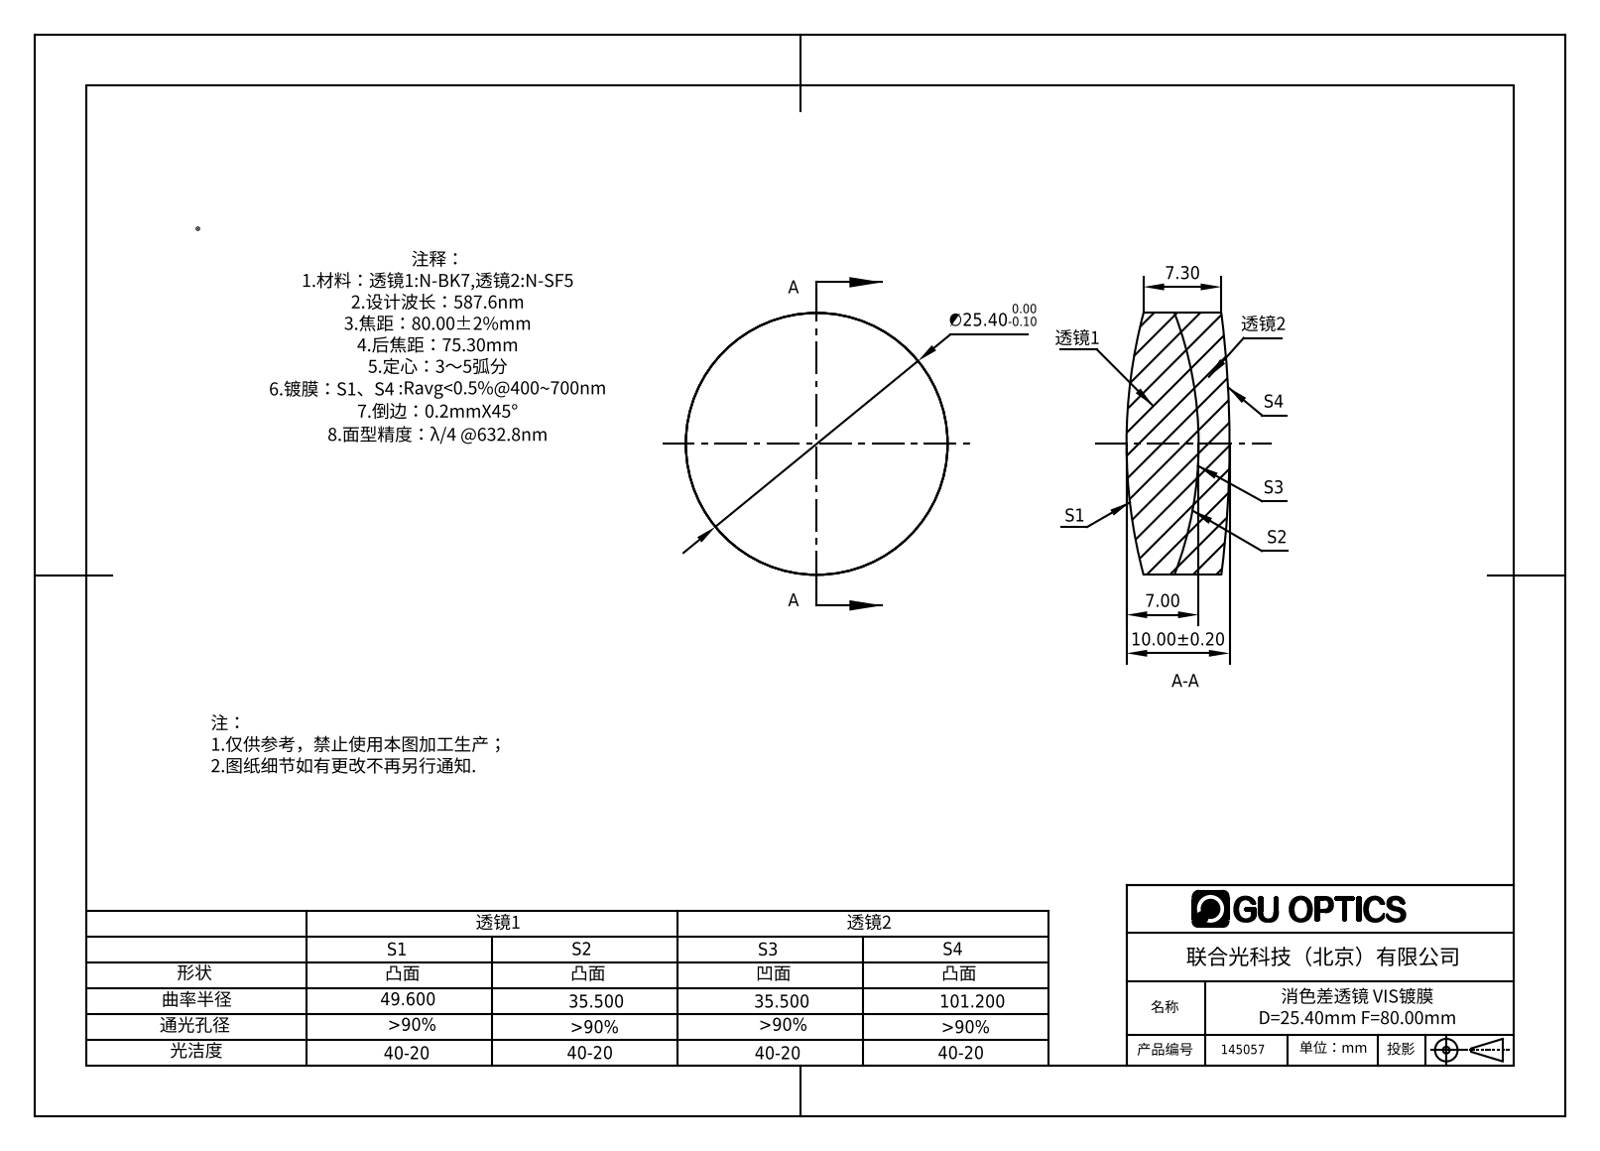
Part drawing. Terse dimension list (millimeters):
name: 145057
written by: SolidWorks 2016 (AUTOMOTIVE_DESIGN)
unit: mm
bodies: 2 solids, 12 faces (0 planar, 4 cylindrical, 8 other)
size: 25.4 × 25.4 × 10
volume: 4 448 mm³; area: 2 674 mm²
bosses: 1× ⌀25.4
